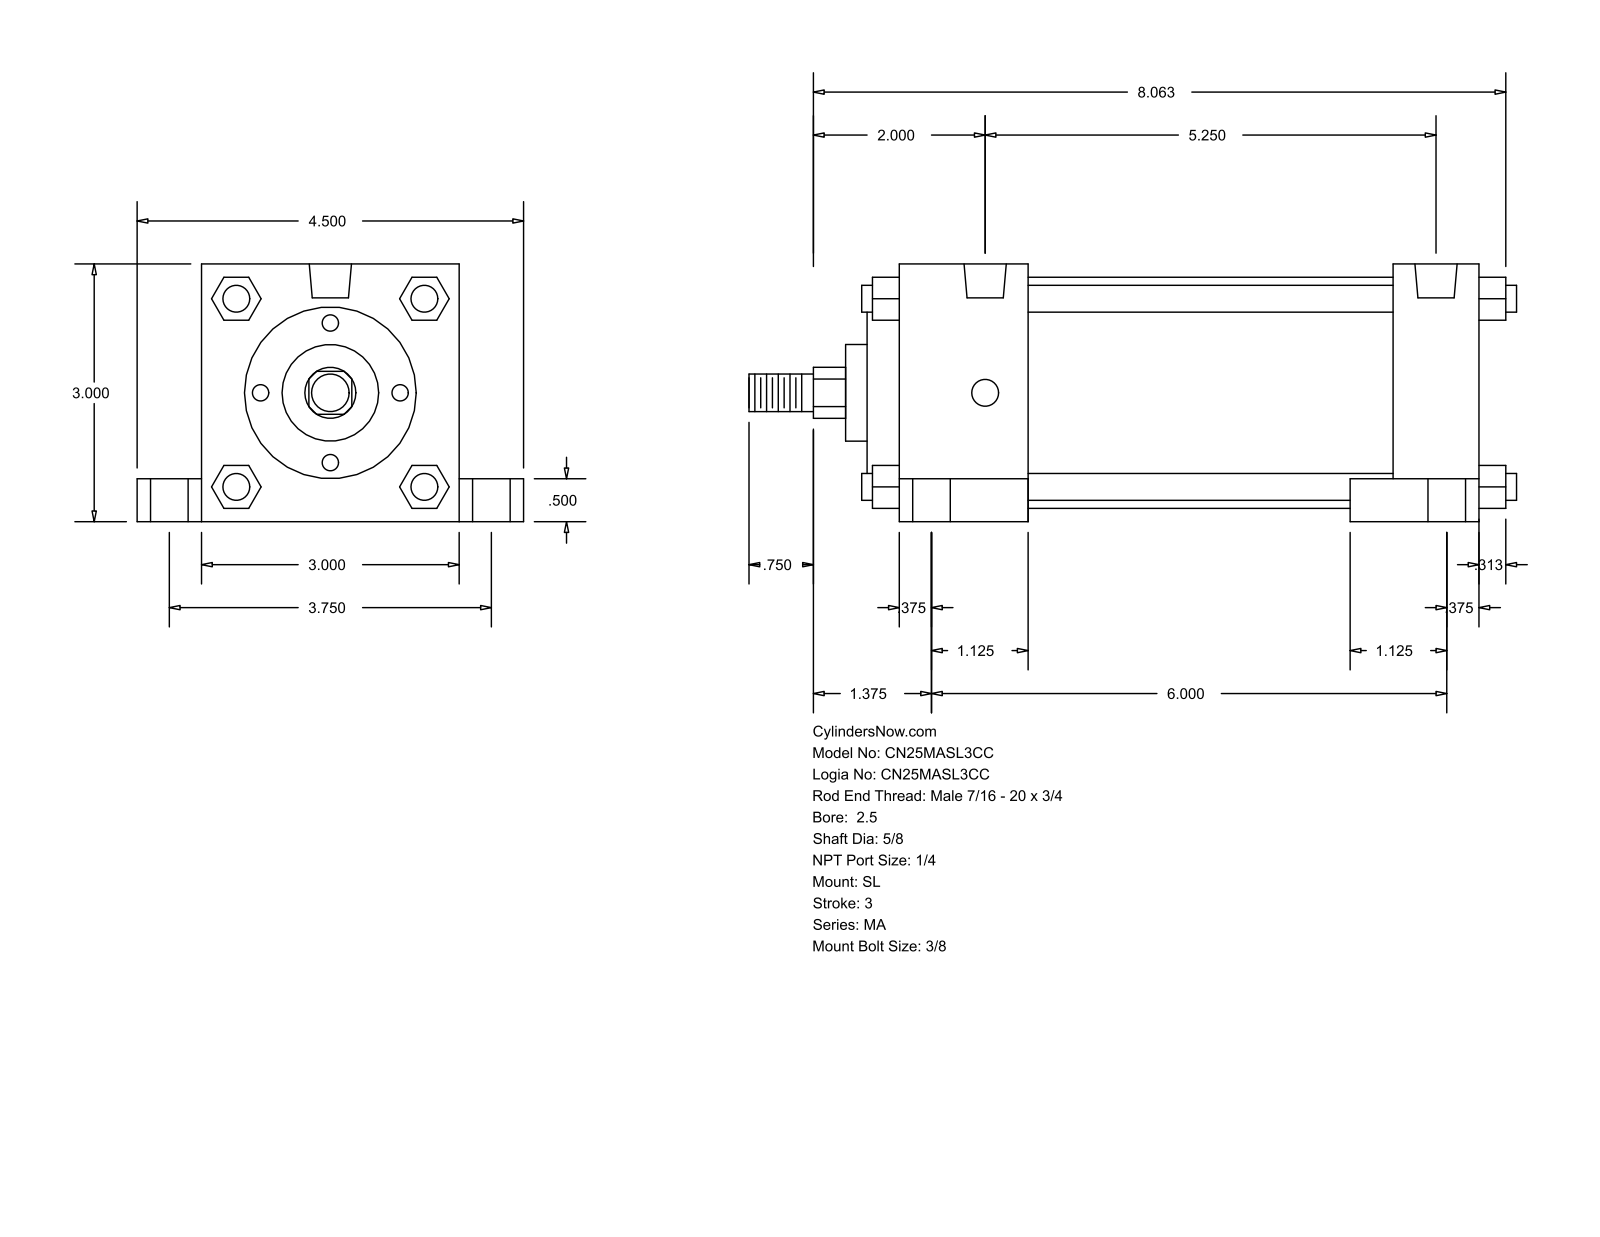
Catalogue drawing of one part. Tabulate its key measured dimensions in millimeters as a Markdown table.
| quantity | value |
| --- | --- |
| part name | MA_SL__0250_0.625 |
| STEP written by | GSSL Pune (CONFIG_CONTROL_DESIGN) |
| units | millimeters |
| bodies | 0 solids, 150 faces (113 planar, 37 cylindrical, 0 other) |
| overall size | 227.01 × 114.3 × 76.2 |
| round holes (diameter × count) | 7.94 × 4, 11.11 × 4, 17.46 × 4, 12.49 × 2 |
| round bosses / shafts (diameter × count) | 7.94 × 4, 68.33 × 1, 50.8 × 1, 28.57 × 1, 15.88 × 1, 11.11 × 1 |
| partial cylindrical surfaces (radius × count) | 7.54 × 1 |
| main face-to-face distances | 76.2, 171.45, 12.7, 107.95, 25.4, 38.1, 133.35, 146.05, 19.05, 63.5 |
| hole center spacings | 47.73, 50.2, 95.24, 133.35, 144.59, 152.4, 156.64, 179.71 |
